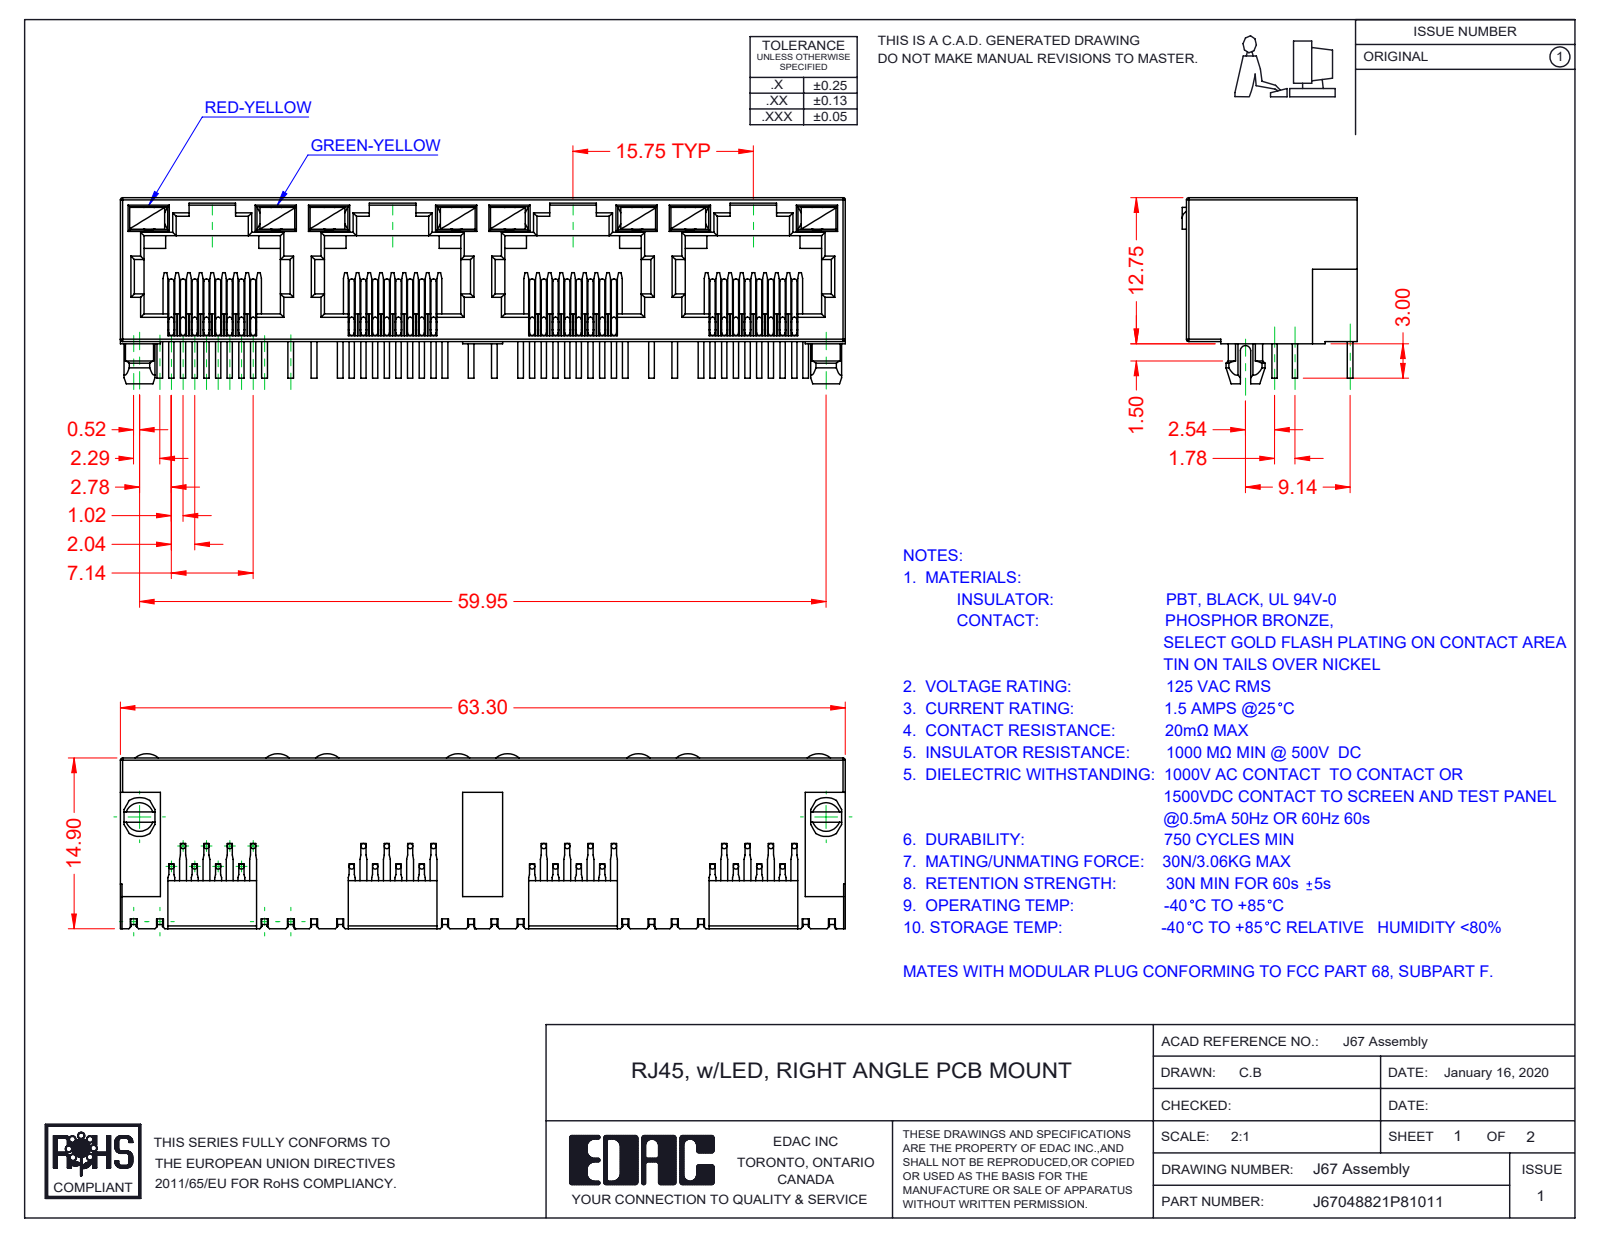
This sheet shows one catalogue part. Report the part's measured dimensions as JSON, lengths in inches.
{"part_name": "J67048822P85011; 67 Insulator; 67 Contacts; 67 LED LH_8-Red-Yellow (+1 more)", "step_written_by": "SolidWorks 2016 (CONFIG_CONTROL_DESIGN)", "units": "inches", "bodies": {"solids": 41, "faces": 2481, "planar": 1781, "cylindrical": 492, "other": 208}, "overall_size": [2.492, 0.64, 0.602], "volume_in3": 0.315, "surface_area_in2": 17.94, "round_bosses_or_shafts": [[0.018, 96]], "partial_cylinders_radius": [[0.008, 66], [0.012, 29], [0.018, 9], [0.061, 8], [0.059, 2], [0.067, 2], [0.014, 1], [0.039, 1]], "face_to_face_distances": [0.02, 0.494, 0.074, 0.035, 0.394, 0.62, 0.039, 0.055, 0.433, 0.468]}
